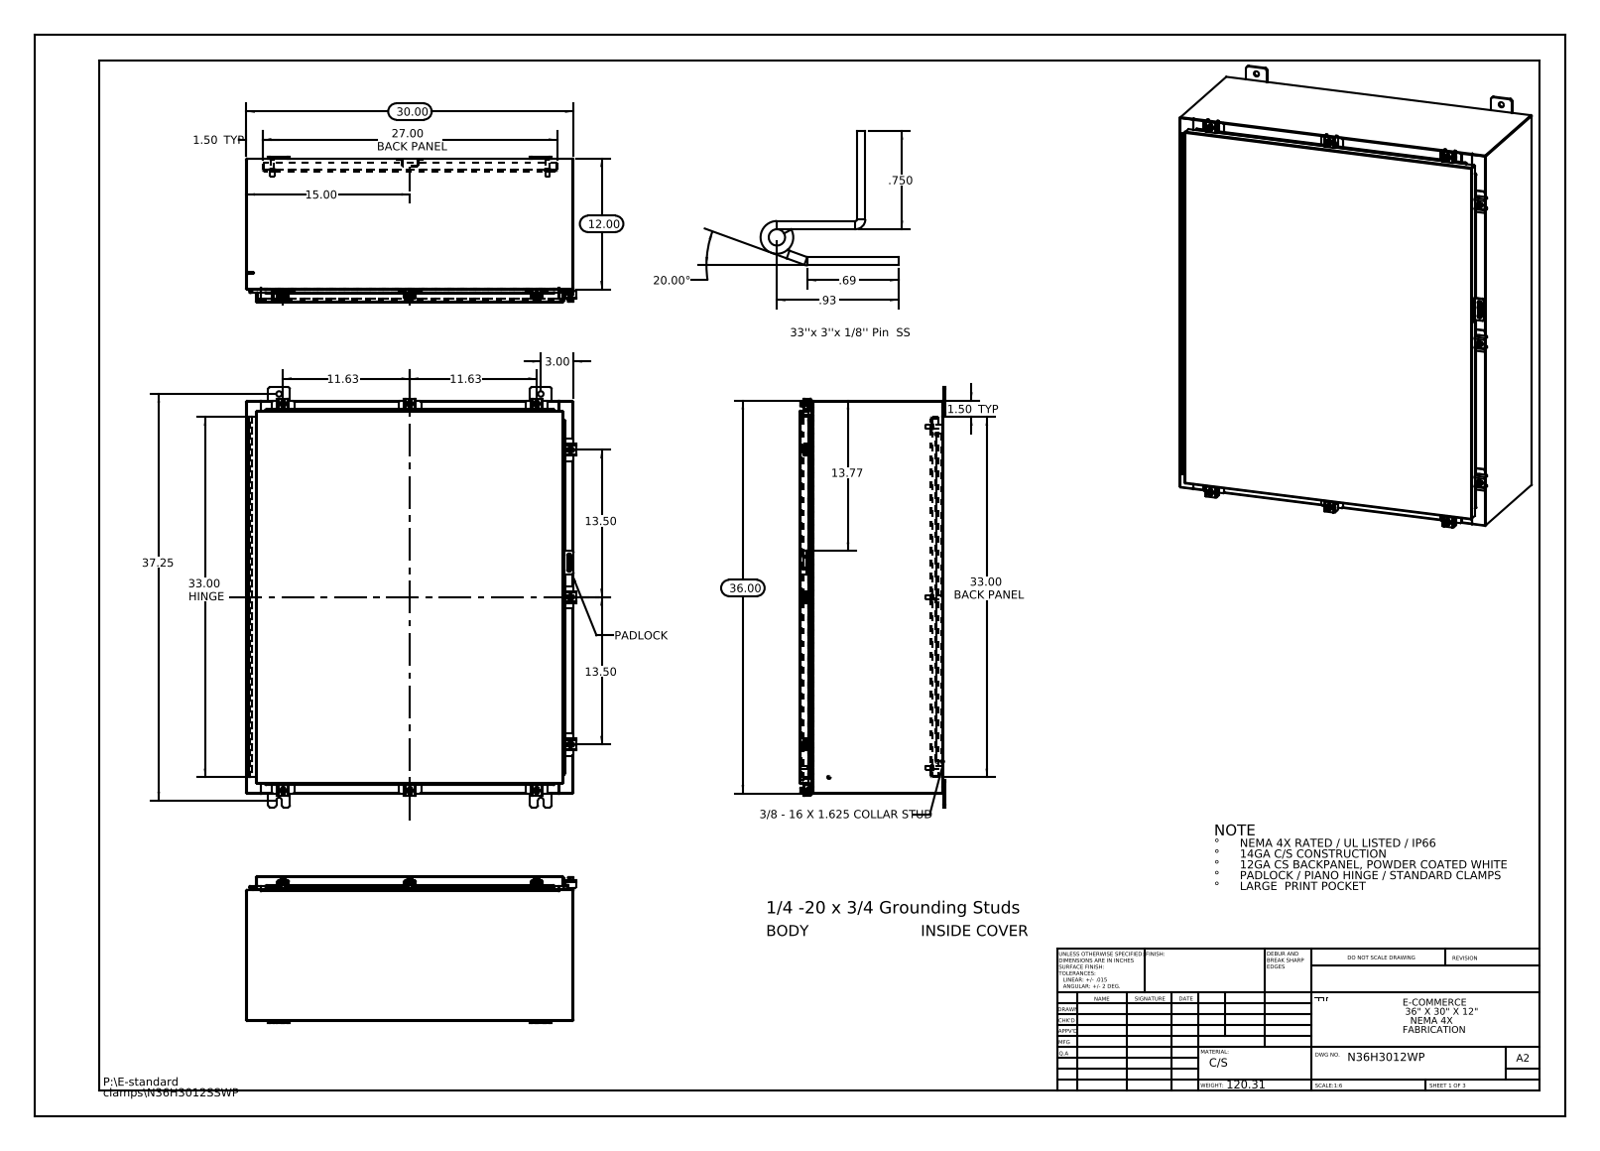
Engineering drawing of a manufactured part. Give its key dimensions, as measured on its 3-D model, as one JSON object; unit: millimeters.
{"part_name": "N36H3012SSWP Clamp Bracket; N36H3012SSWP Mounting Studs; N36H3012SSWP Backpanel; N36H3012SSWP Clamp Top (+8 more)", "step_written_by": "SolidWorks 2013 (CONFIG_CONTROL_DESIGN)", "units": "millimeters", "bodies": {"solids": 67, "faces": 2482, "planar": 1294, "cylindrical": 1036, "other": 152}, "overall_size": [977.9, 767.4, 340.1], "volume_mm3": 6912000, "surface_area_mm2": 6821000, "round_holes": [[12.7, 10], [5.4, 9], [6.6, 9], [3.2, 2]], "round_bosses_or_shafts": [[6.4, 10], [12.7, 9], [10.1, 9], [15.9, 6], [9.5, 6], [8.4, 6], [8, 2], [6, 2]], "partial_cylinders_radius": [[1.5, 42], [0.3, 31], [2.2, 25], [4.8, 24], [3, 18], [3.6, 18], [1.3, 13], [2, 12]], "face_to_face_distances": [1.9, 333.4, 331.5, 335.3, 2.6, 308, 25.4, 27.3, 306.1, 29.9], "hole_center_spacings": [396.9, 451, 754.2, 847.5, 947.6, 641.4, 900.5, 47.2]}
